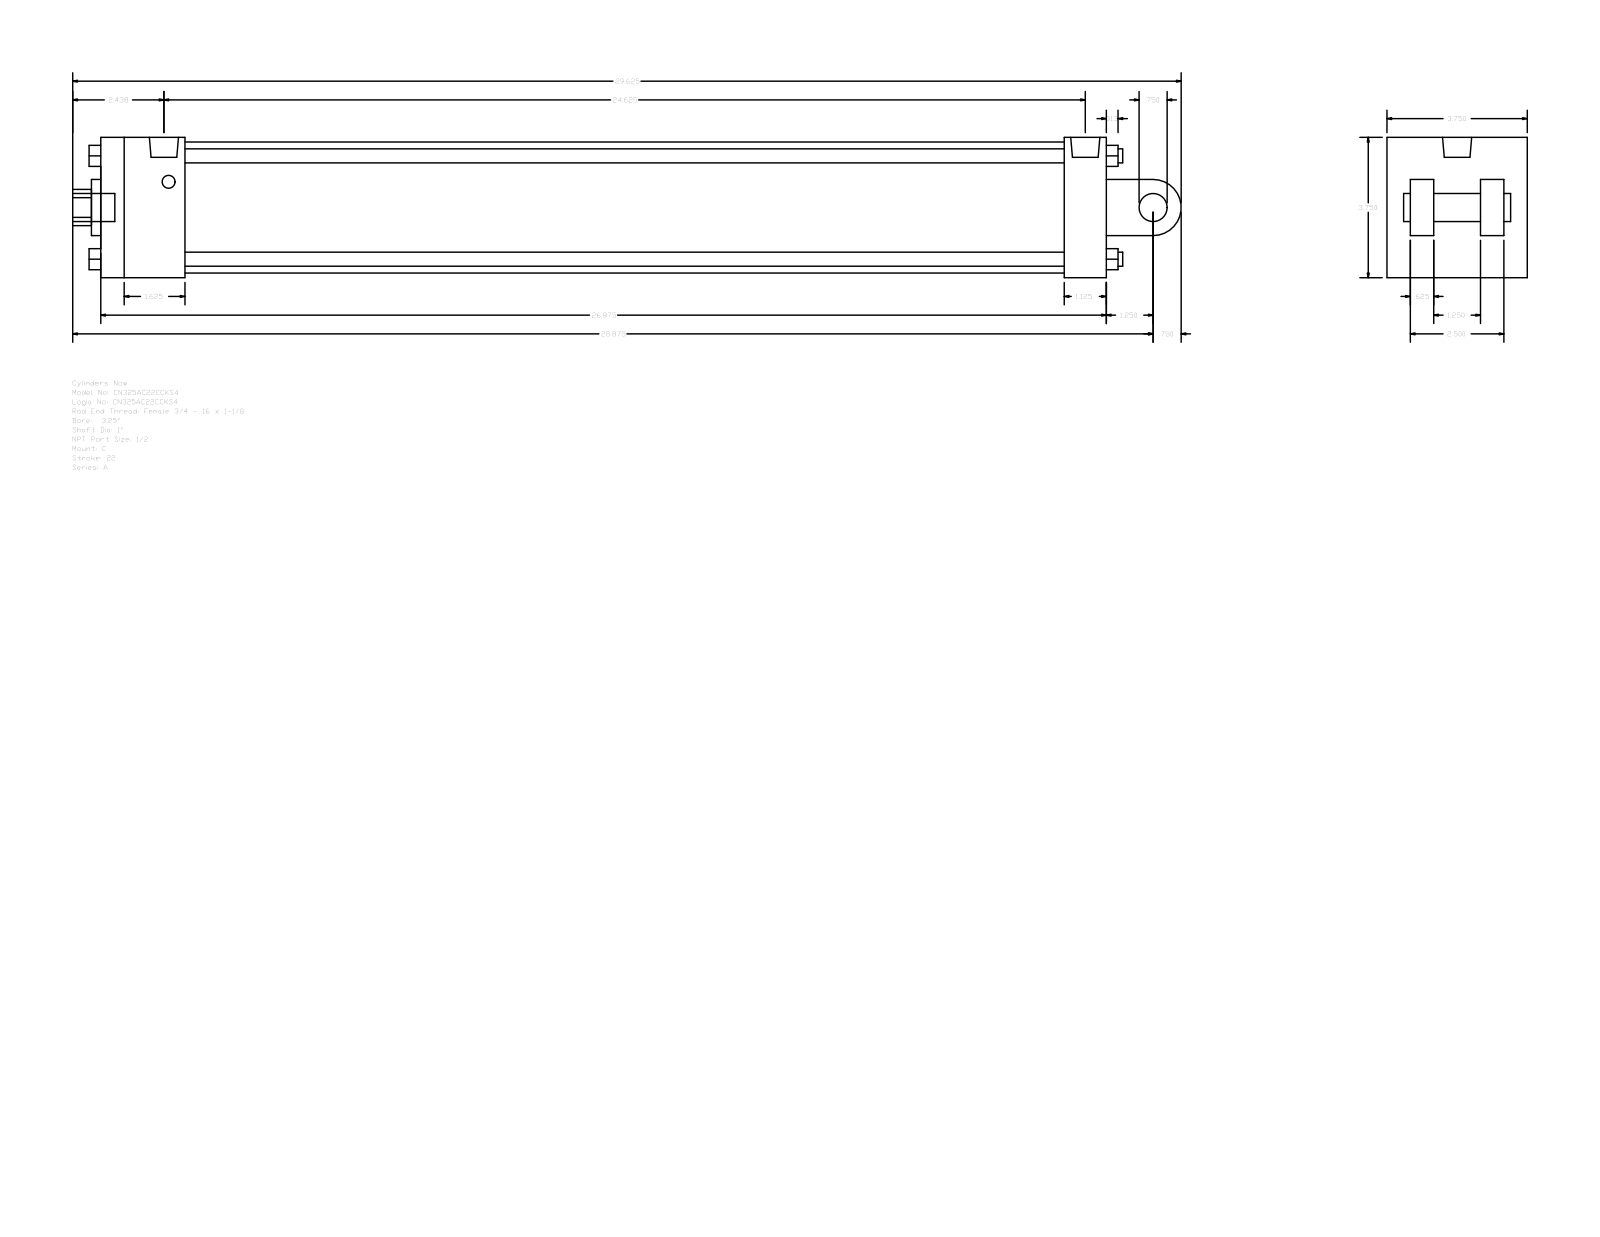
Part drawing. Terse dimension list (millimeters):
name: A_C__0325_1
written by: GSSL Pune (CONFIG_CONTROL_DESIGN)
unit: mm
bodies: 0 solids, 135 faces (102 planar, 33 cylindrical, 0 other)
size: 752.48 × 95.25 × 95.25
holes: 2× ⌀8.73, 1× ⌀19.77, 1× ⌀25.4, 1× ⌀38.1, 1× ⌀88.9
bosses: 4× ⌀9.53, 2× ⌀19.05, 2× ⌀8.73, 1× ⌀19.77
rounds: 1× R12.29, 1× R19.05
face distances: 95.24, 682.62, 15.87, 63.5, 28.57, 47.63, 31.74, 79.37, 66.67, 654.05
hole spacings: 3.18
